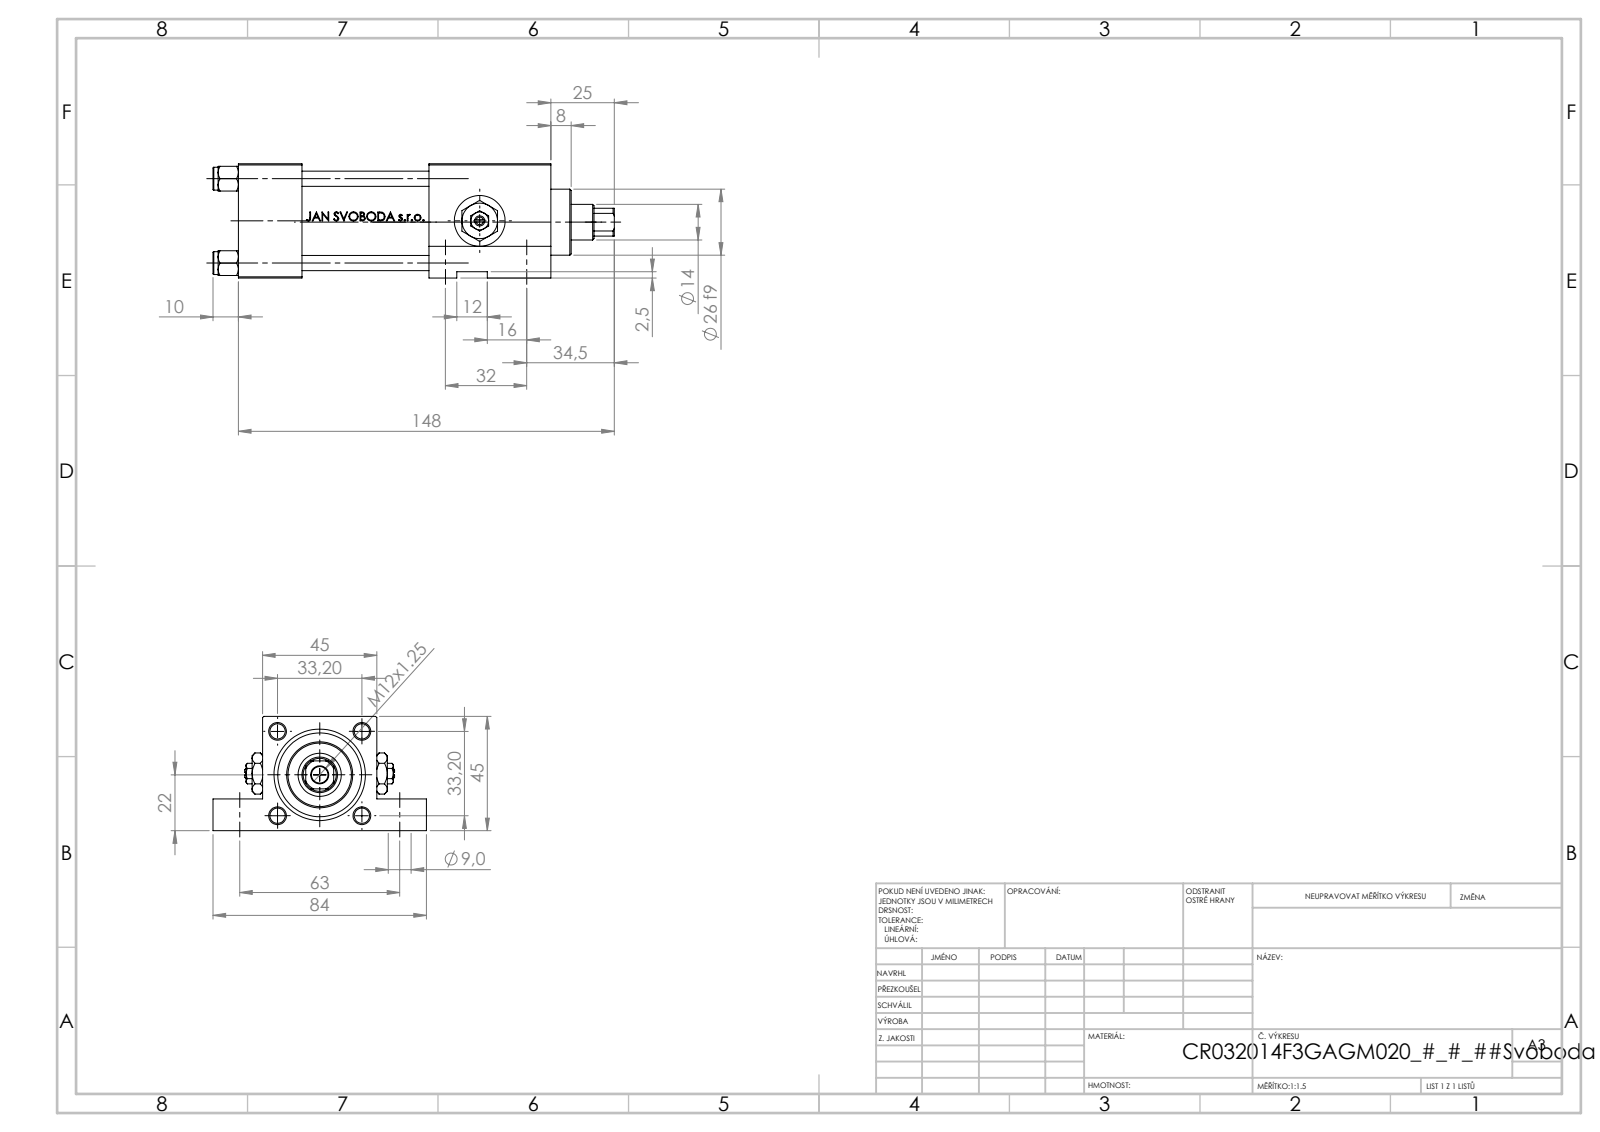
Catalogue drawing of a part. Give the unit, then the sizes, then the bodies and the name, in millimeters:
Units: millimetres
Overall size (bounding box): 158 × 84 × 45
Round holes (diameter × count): ⌀6 ×4, ⌀9 ×4, ⌀7 ×3, ⌀20 ×3, ⌀13.16 ×2, ⌀6.5 ×1, ⌀13 ×1, ⌀14 ×1, ⌀17 ×1, ⌀24 ×1, ⌀32 ×1, ⌀33 ×1
Round bosses / shafts (diameter × count): ⌀9 ×4, ⌀38 ×1, ⌀26 ×1
Partial cylindrical surfaces — rounded edges, fillets, slot ends (radius × count): R6.5 ×1
Main face-to-face distances: 45, 25, 98, 123, 50, 32.5, 75, 48, 12.5, 10
Hole centre spacings: 33.2, 23.13, 23.83, 32, 46.95, 63, 70.66, 75.85
Volume: 211 986 mm³ · Surface area: 74 323 mm²
Bodies: 13 solids, 1195 faces (481 planar, 132 cylindrical, 582 other)
Part name (STEP PRODUCT): V215CR_VCP_F; Zatka_pro_OIL_PORT; V215_VC_A; NUT_M5_F (+2 more)
STEP written by: SolidWorks 2019 (CONFIG_CONTROL_DESIGN)
